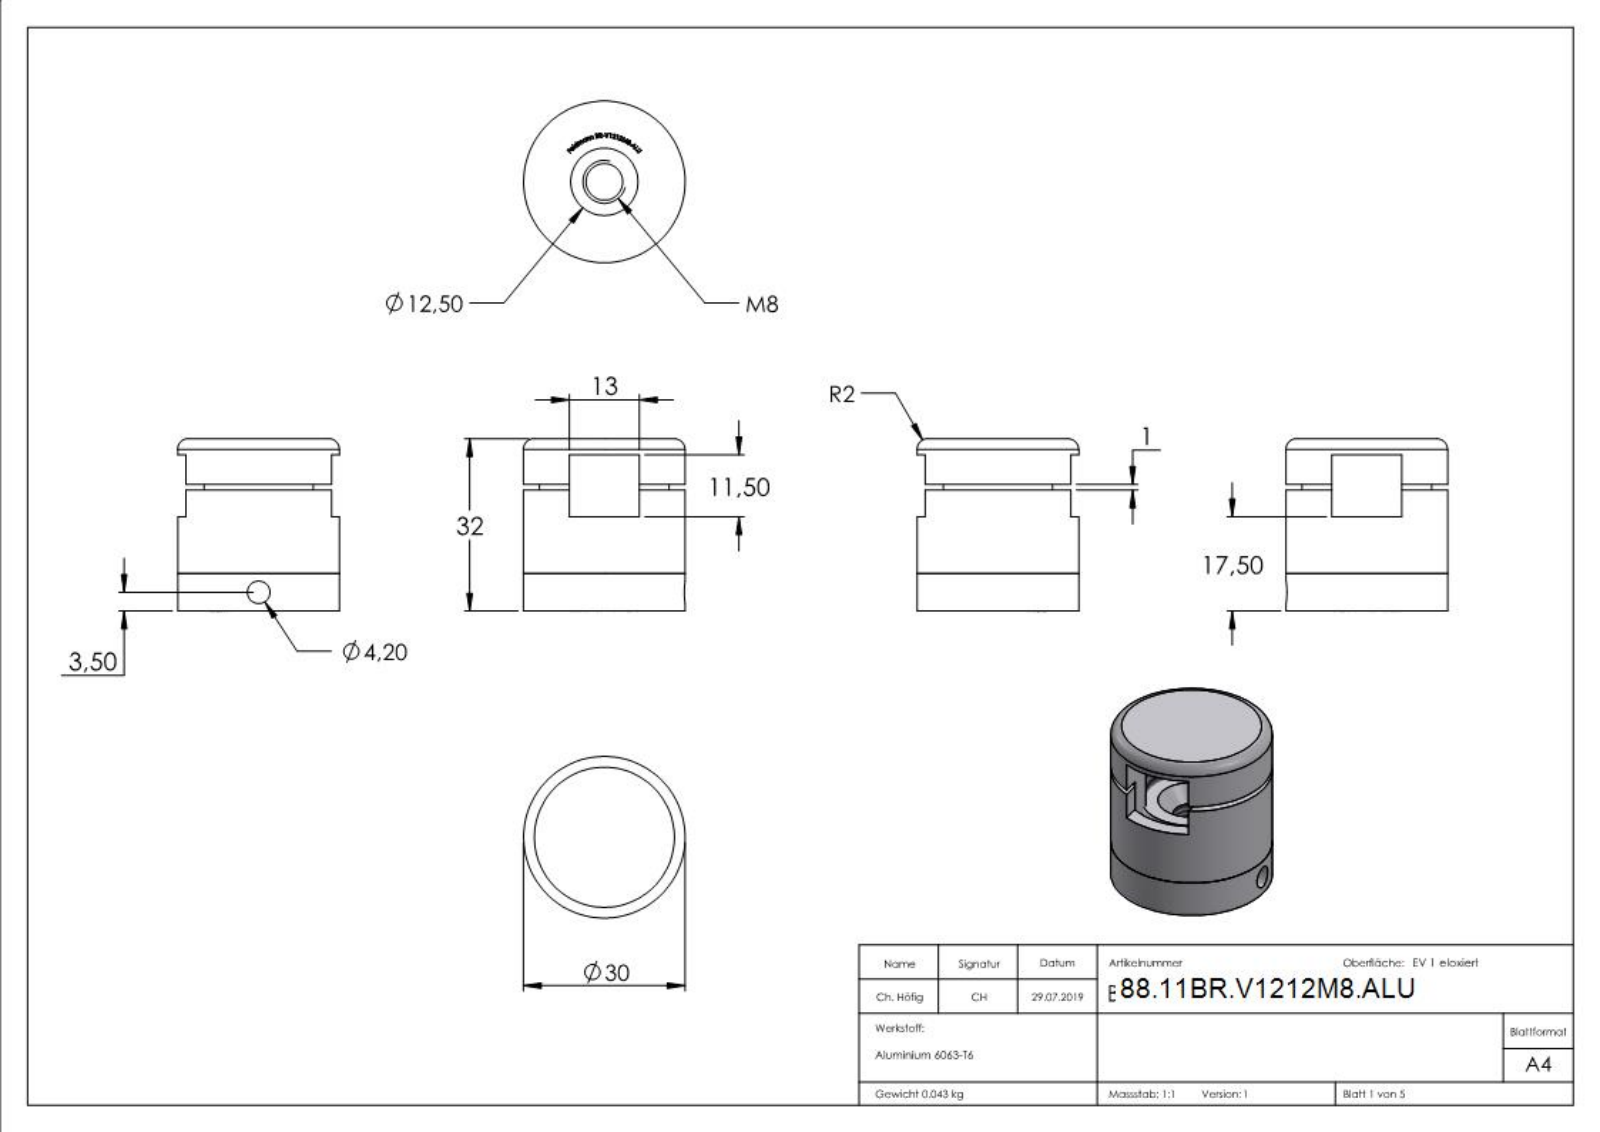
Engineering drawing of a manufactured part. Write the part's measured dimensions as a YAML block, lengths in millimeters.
part_name: "BR-R1XM8-XXX Teil2; BR-R1XM8-XXX Teil1; BR-R1XM8-XXX Teil1_BR-1XM8-ALU Teil1; BR-V1212M8-ALU (+3 more)"
step_written_by: "SolidWorks 2015 (CONFIG_CONTROL_DESIGN)"
units: millimeters
bodies: {solids: 3, faces: 326, planar: 192, cylindrical: 12, other: 122}
overall_size: [64.34, 30, 30]
volume: 15892
surface_area: 9620
round_holes:
  - {diameter: 4.2, count: 1}
  - {diameter: 6.8, count: 1}
  - {diameter: 12.5, count: 1}
  - {diameter: 24.2, count: 1}
round_bosses_or_shafts:
  - {diameter: 30, count: 1}
  - {diameter: 20, count: 1}
partial_cylinders:
  - {radius: 8.75, count: 1}
  - {radius: 12.05, count: 1}
face_to_face_distances: [25, 7, 32, 13, 3, 29, 22, 16, 6.5, 8.5]
